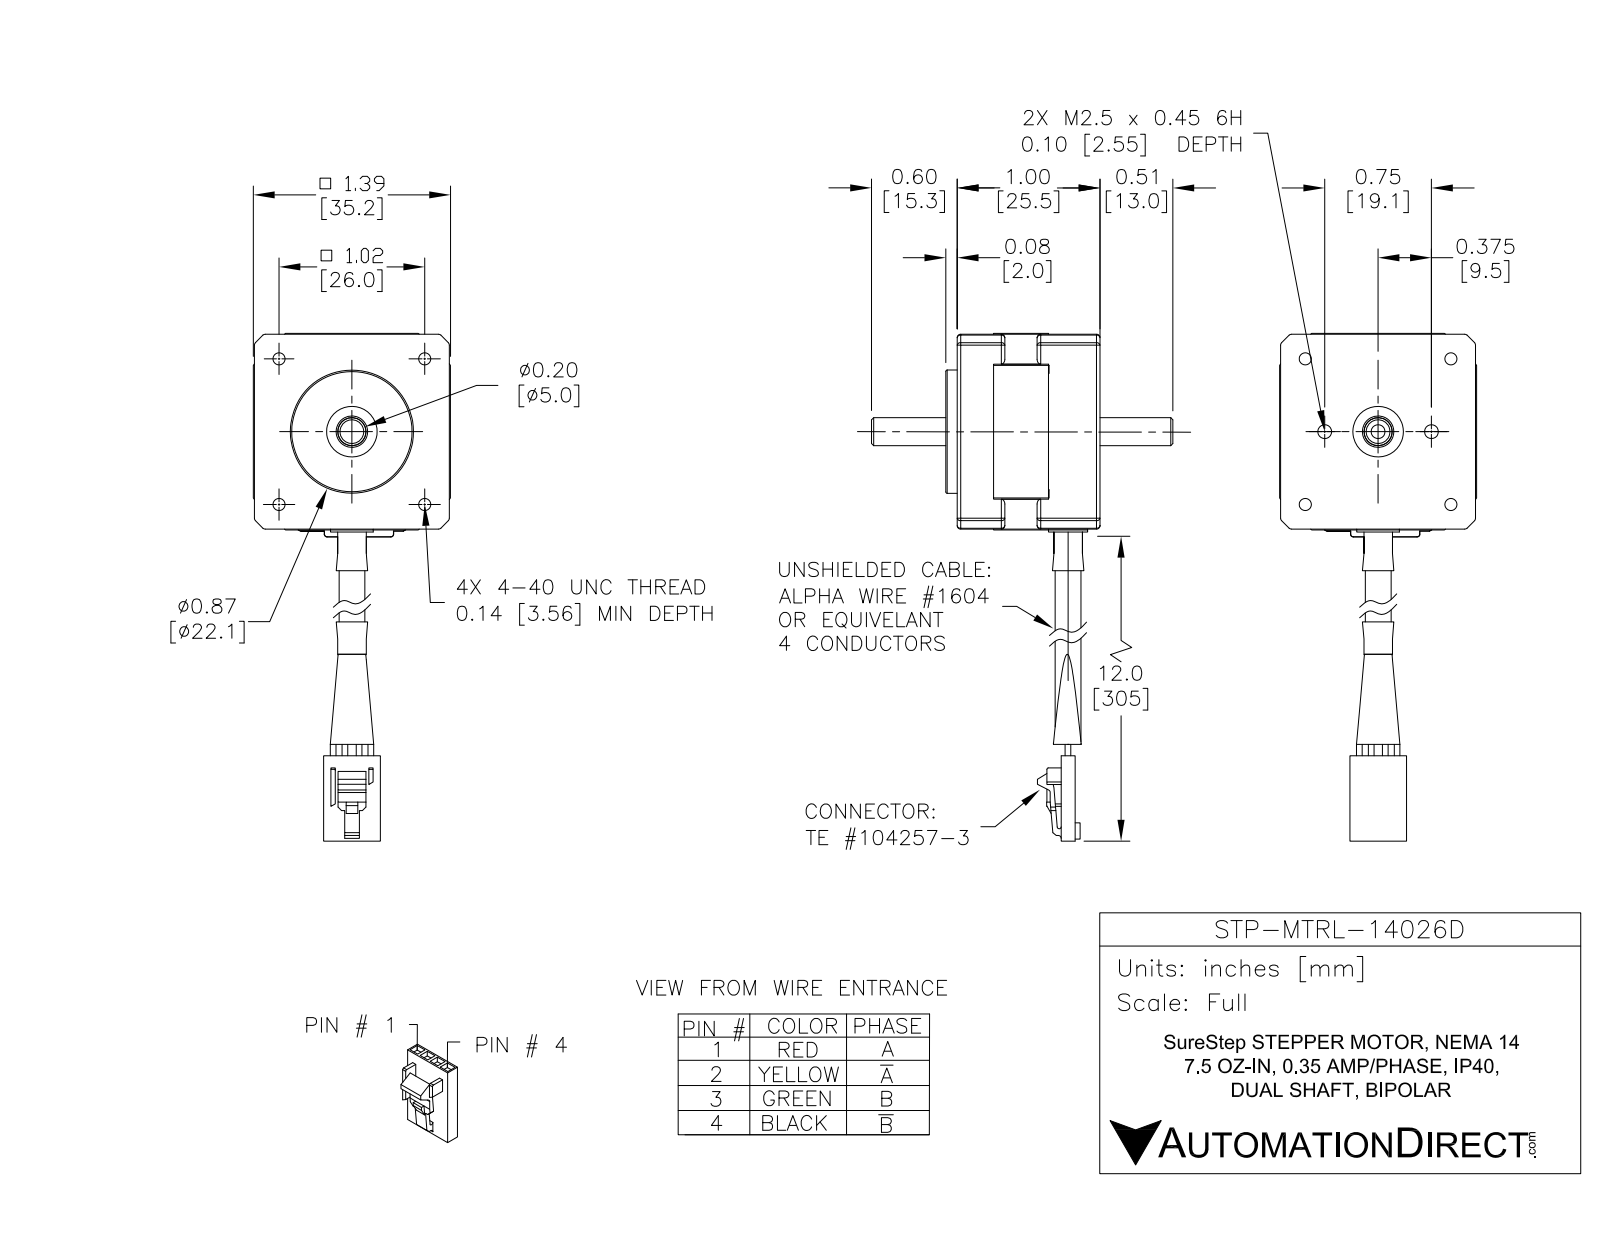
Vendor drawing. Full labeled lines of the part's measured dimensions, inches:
Part name (STEP PRODUCT): STP-MTRL-14026D
STEP written by: SolidWorks 2017 (AUTOMOTIVE_DESIGN)
Units: inches
Bodies: 10 solids, 564 faces (292 planar, 180 cylindrical, 92 other)
Overall size (bounding box): 13.447 × 2.118 × 1.381
Volume: 1.276 in³ · Surface area: 32.67 in²
Round holes (diameter × count): ⌀0.226 ×4, ⌀0.079 ×2, ⌀0.085 ×2, ⌀0.085 ×2, ⌀0.197 ×1, ⌀0.28 ×1, ⌀0.285 ×1, ⌀0.32 ×1, ⌀0.422 ×1, ⌀0.52 ×1, ⌀0.63 ×1, ⌀0.9 ×1
Round bosses / shafts (diameter × count): ⌀0.04 ×4, ⌀0.205 ×3, ⌀0.05 ×2, ⌀0.866 ×1, ⌀0.72 ×1, ⌀0.477 ×1, ⌀0.308 ×1, ⌀0.307 ×1
Partial cylindrical surfaces — rounded edges, fillets, slot ends (radius × count): R0.025 ×24, R0.02 ×10, R0.01 ×3, R0.014 ×1, R0.797 ×1, R0.798 ×1, R0.829 ×1, R0.833 ×1
Main face-to-face distances: 1.37, 1.376, 1.24, 0.065, 1.305, 0.104, 1.004, 0.9, 1.311, 0.07
Hole centre spacings: 1.024, 0.53, 0.724, 1.024, 1.448, 0.375, 0.375, 0.75
